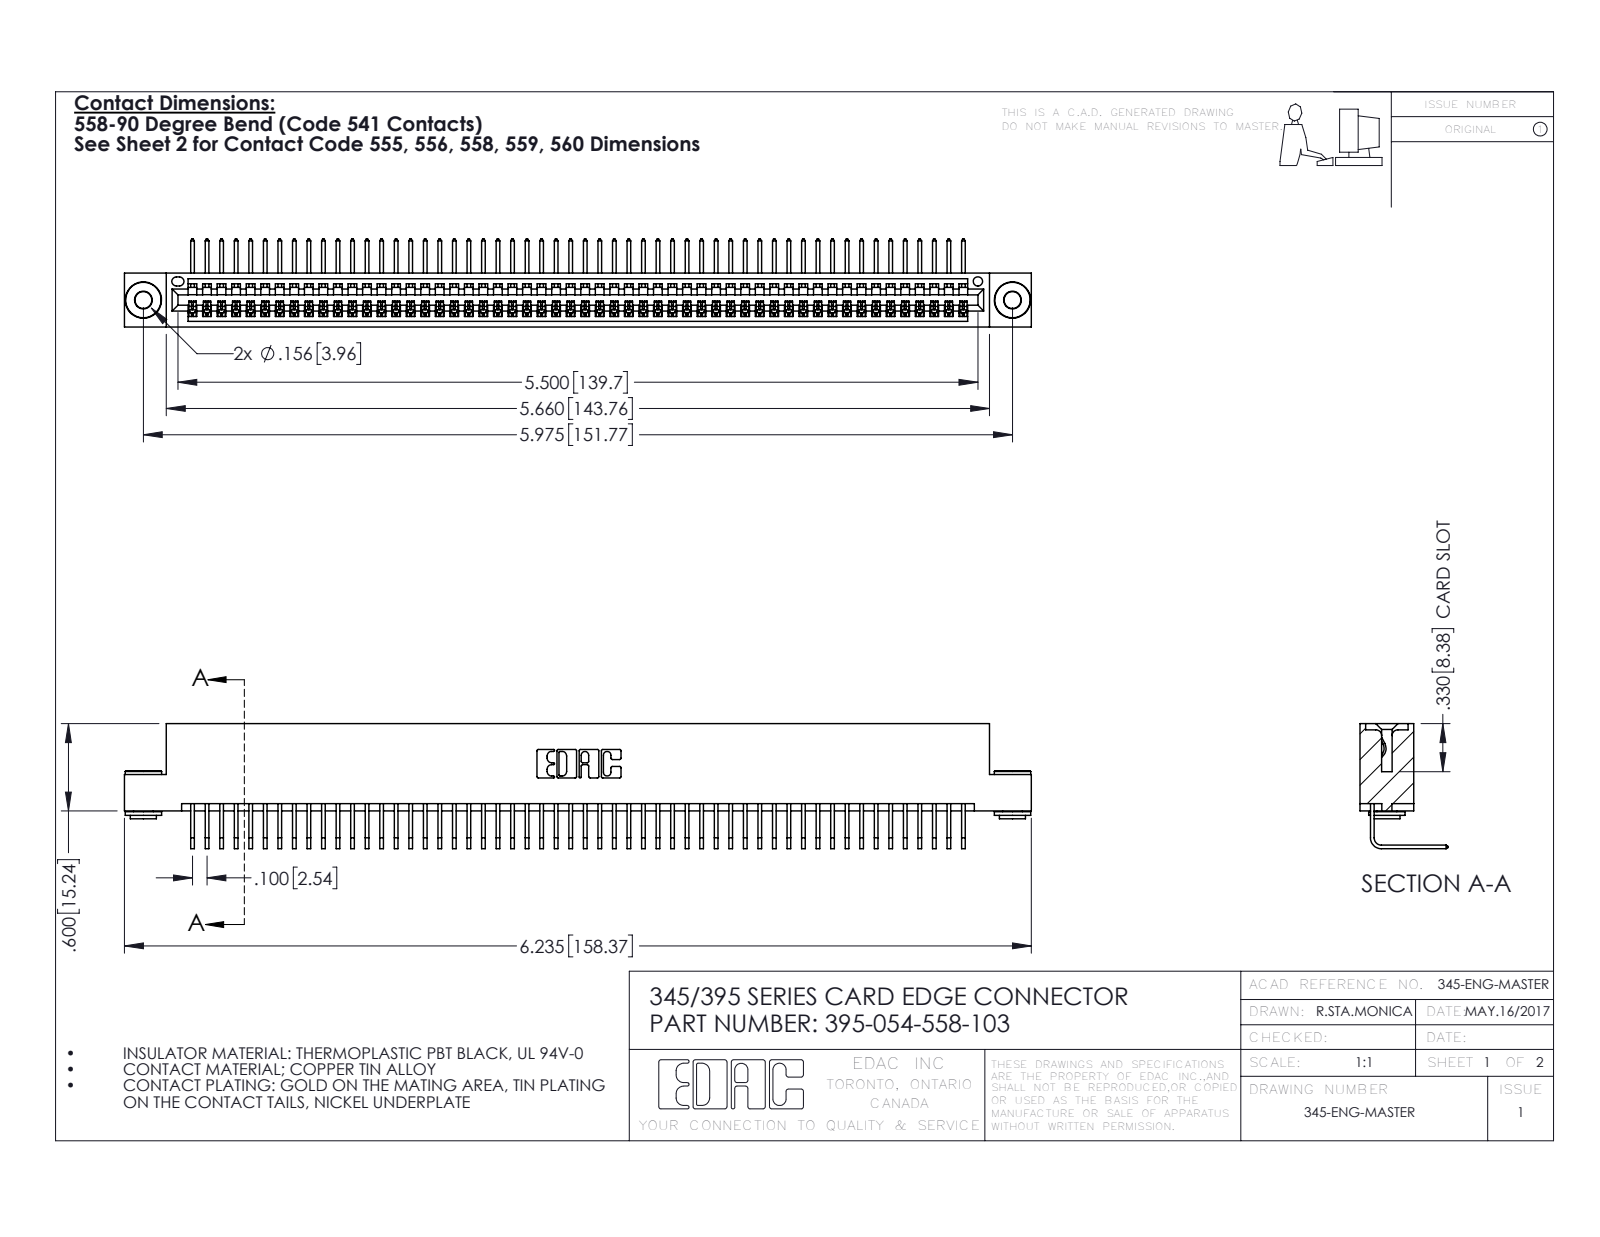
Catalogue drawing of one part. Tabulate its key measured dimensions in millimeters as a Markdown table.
| quantity | value |
| --- | --- |
| part name | 395-054-558-103; 345 Part_Flush Mounting Lugs - 0.156 Dia-TH; 345-292-001_558 Tail - 2; 345-250-002_345-250-002-102 |
| STEP written by | SolidWorks 2016 (CONFIG_CONTROL_DESIGN) |
| units | millimeters |
| bodies | 57 solids, 3404 faces (2358 planar, 1038 cylindrical, 8 other) |
| overall size | 158.4 × 21.8 × 15.4 |
| volume | 15 300 mm³ |
| surface area | 21 820 mm² |
| round holes (diameter × count) | 2.9 × 2, 4 × 2, 1.6 × 1 |
| round bosses / shafts (diameter × count) | 6.4 × 2, 4.6 × 2, 3.5 × 2 |
| partial cylindrical surfaces (radius × count) | 0.2 × 108, 0.3 × 22, 0.2 × 6, 0.8 × 6, 0.7 × 3, 0.8 × 2, 1 × 2, 0.4 × 1 |
| main face-to-face distances | 1.8, 7.6, 9.4, 5.1, 0.6, 2.5, 6.9, 5.7, 3.8, 1.8 |
| hole center spacings | 6.9, 145.8, 151.8 |
